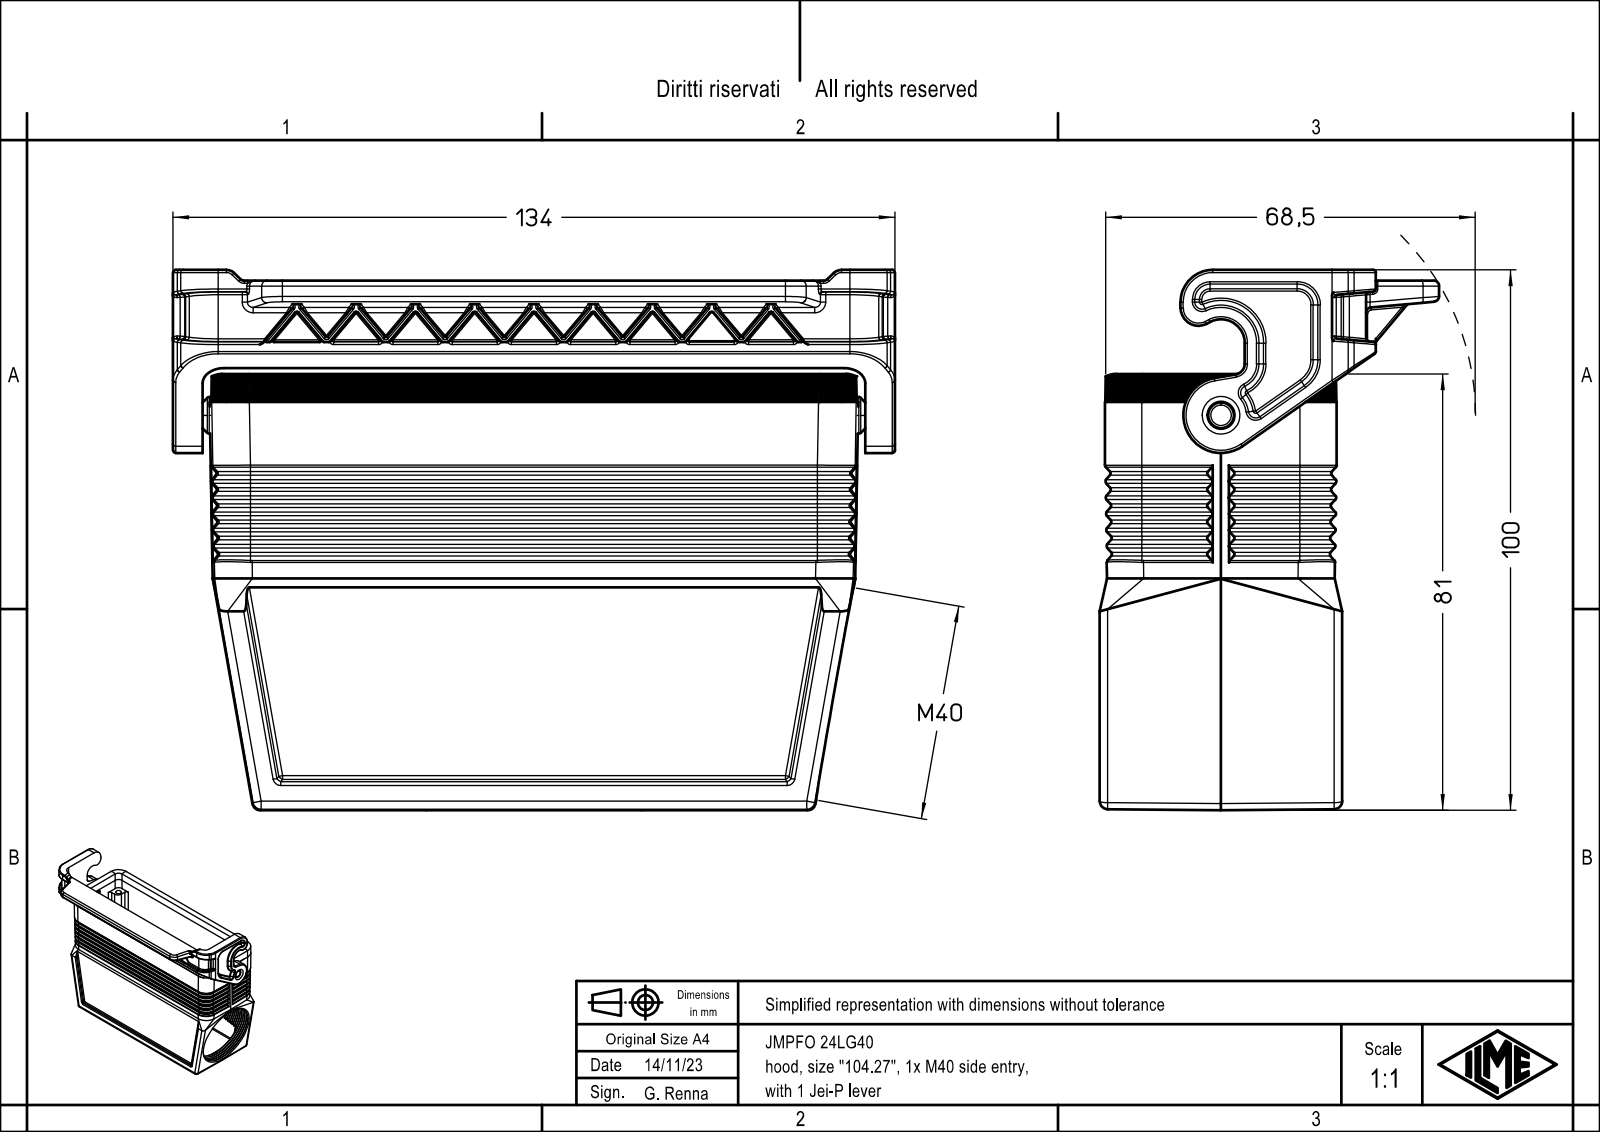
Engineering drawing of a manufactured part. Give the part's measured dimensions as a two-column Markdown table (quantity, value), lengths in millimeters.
| quantity | value |
| --- | --- |
| part name | JMPFO 24LG40 |
| STEP written by | Creo Elements/Direct Modeling 20.1B 02-Apr-2019 (C) Parametric Technology GmbH (AUTOMOTIVE_DESIGN) |
| units | millimeters |
| bodies | 1 solid, 1245 faces (361 planar, 465 cylindrical, 419 other) |
| overall size | 134 × 100.25 × 63 |
| volume | 126 826 mm³ |
| surface area | 69 297 mm² |
| round holes (diameter × count) | 3 × 4, 3.5 × 4, 4.8 × 1, 38.6 × 1 |
| round bosses / shafts (diameter × count) | 6.8 × 1 |
| partial cylindrical surfaces (radius × count) | 0.5 × 147, 0.3 × 126, 1 × 27, 1.5 × 22, 0.33 × 15, 7 × 13, 3 × 12, 4 × 8 |
| main face-to-face distances | 3.75, 39.25, 35.5, 43, 2, 7, 4, 3.25, 42.5, 46.25 |
| hole center spacings | 27, 104, 107.45 |
